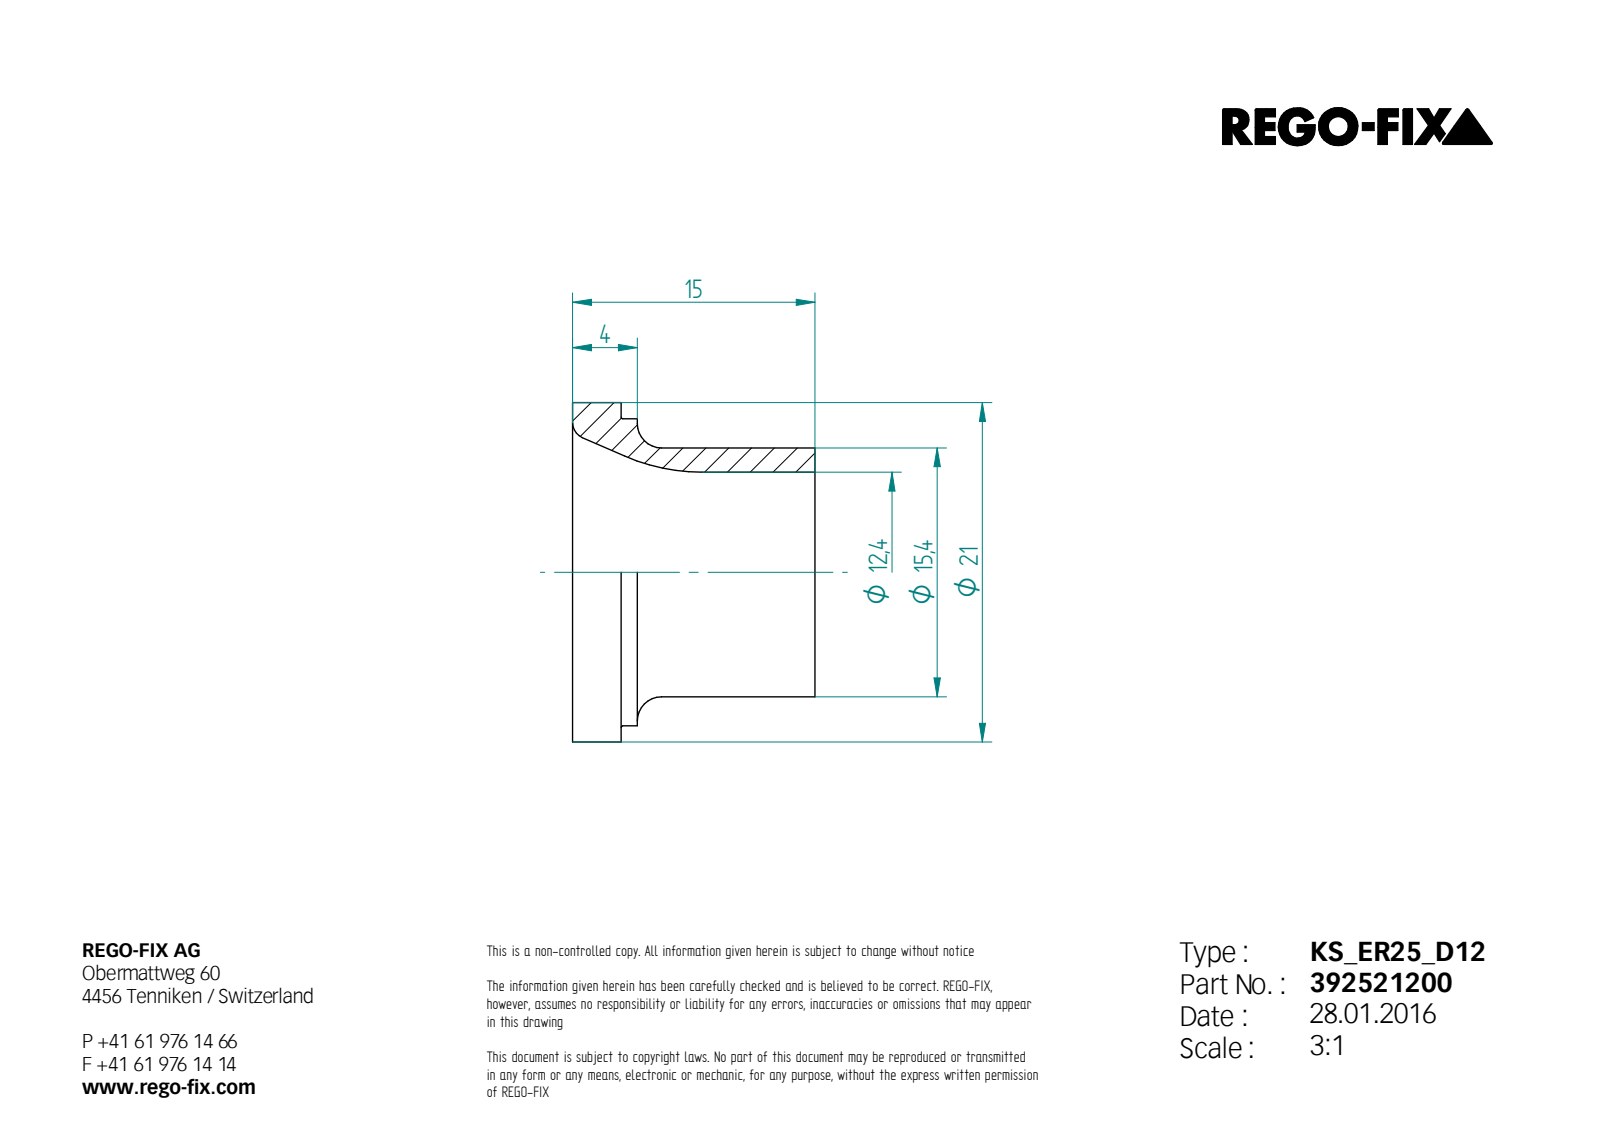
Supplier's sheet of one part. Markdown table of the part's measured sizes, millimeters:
| quantity | value |
| --- | --- |
| STEP written by | Unknown (AUTOMOTIVE_DESIGN) |
| units | millimeters |
| bodies | 1 solid, 13 faces (4 planar, 4 cylindrical, 5 other) |
| overall size | 21 × 21 × 15 |
| volume | 1 274 mm³ |
| surface area | 1 738 mm² |
| round holes (diameter × count) | 12.4 × 1 |
| round bosses / shafts (diameter × count) | 21 × 1, 19 × 1, 15.4 × 1 |
| main face-to-face distances | 15, 3, 12, 4, 1, 11 |
